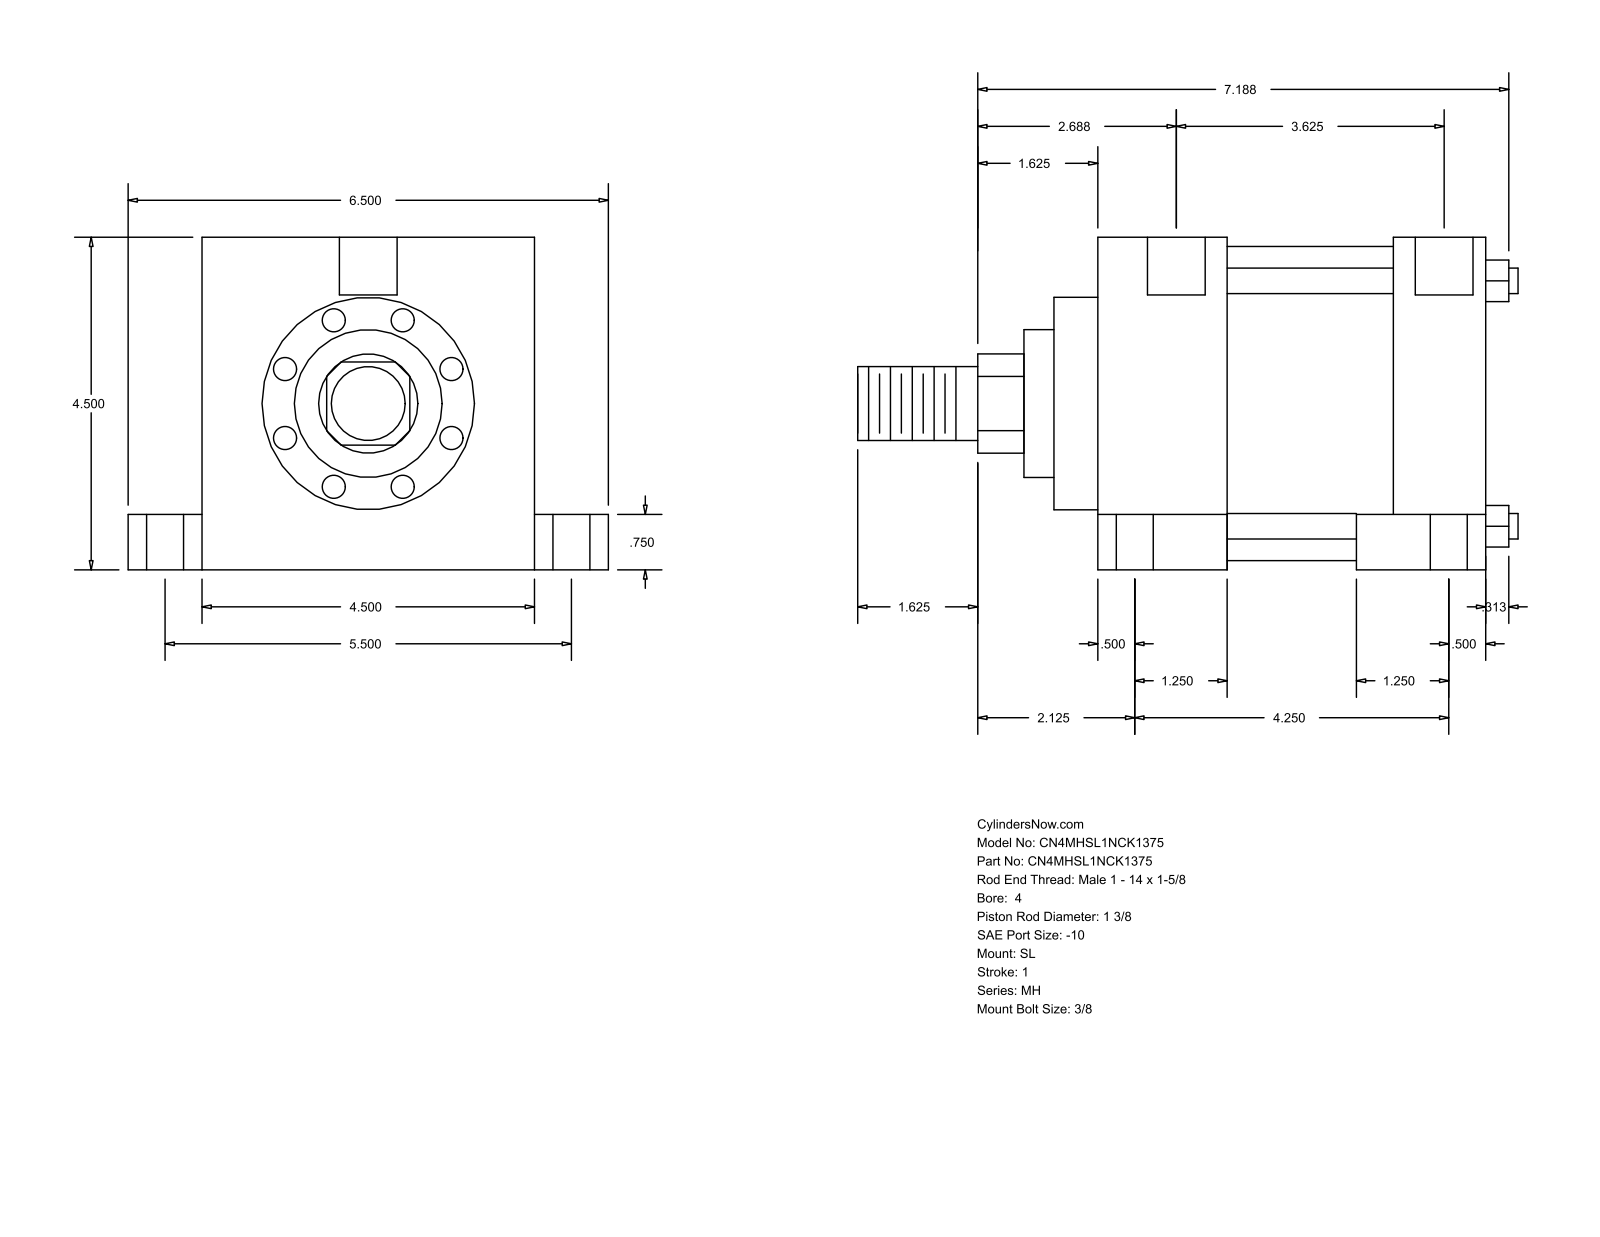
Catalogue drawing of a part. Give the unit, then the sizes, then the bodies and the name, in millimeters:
Units: millimetres
Overall size (bounding box): 227.01 × 165.1 × 114.3
Round holes (diameter × count): ⌀8.73 ×4, ⌀12.7 ×4, ⌀19.05 ×4, ⌀19.84 ×2
Round bosses / shafts (diameter × count): ⌀8.76 ×4, ⌀107.95 ×1, ⌀73.03 ×1, ⌀50.8 ×1, ⌀34.92 ×1, ⌀25.4 ×1
Partial cylindrical surfaces — rounded edges, fillets, slot ends (radius × count): R17.06 ×1
Main face-to-face distances: 114.3, 133.35, 44.45, 88.9, 101.61, 57.16, 31.74, 25.4, 139.7, 19.05
Hole centre spacings: 1.59, 69.85, 69.87, 70.99, 71.29, 93.67, 95.26, 107.95
Bodies: 0 solids, 110 faces (77 planar, 33 cylindrical, 0 other)
Part name (STEP PRODUCT): MH_SL__0400_1.375
STEP written by: GSSL Pune (CONFIG_CONTROL_DESIGN)
